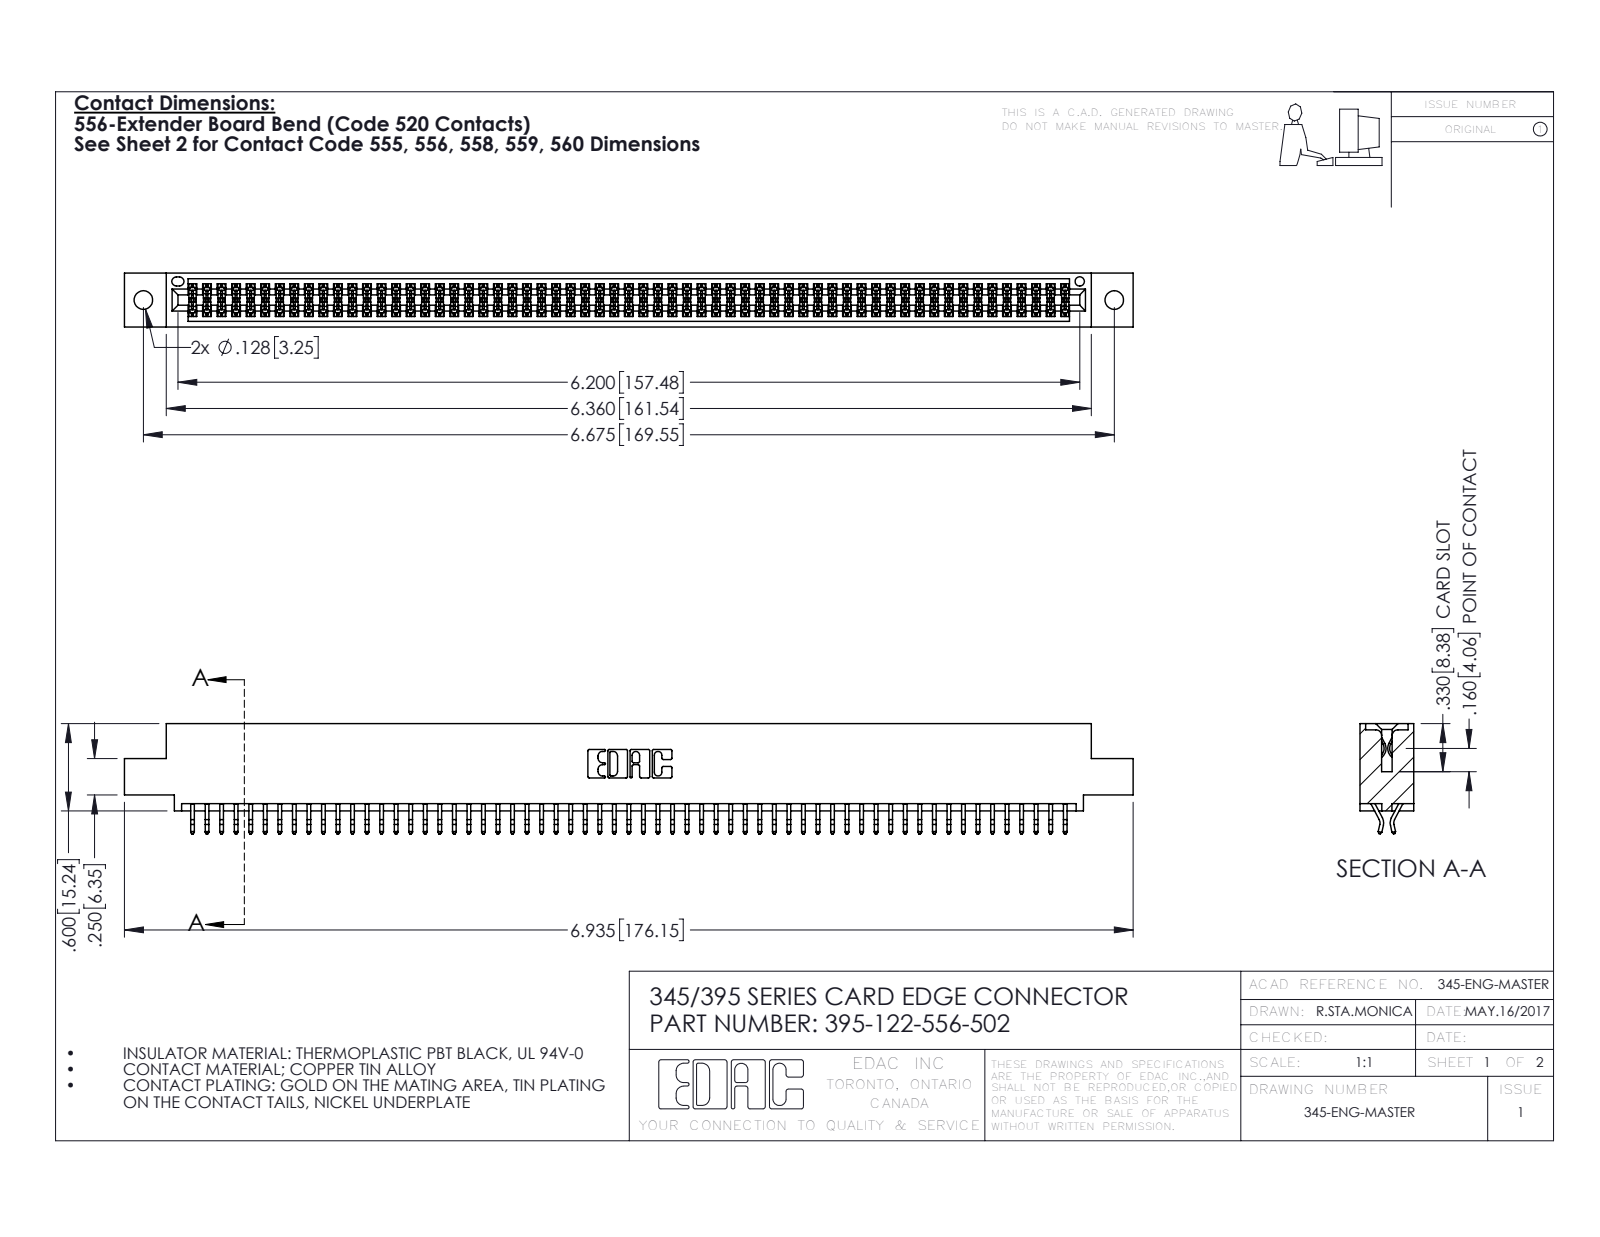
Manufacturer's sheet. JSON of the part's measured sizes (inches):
{"part_name": "395-122-556-502; 345 Part_0.110 Offset - 0.128 Dia; 345-292-001_556 Tail", "step_written_by": "SolidWorks 2016 (CONFIG_CONTROL_DESIGN)", "units": "inches", "bodies": {"solids": 123, "faces": 6962, "planar": 4598, "cylindrical": 2364, "other": 0}, "overall_size": [6.935, 0.757, 0.37], "volume_in3": 1.048, "surface_area_in2": 39.47, "round_holes": [[0.128, 2], [0.064, 1]], "partial_cylinders_radius": [[0.006, 183], [0.01, 22], [0.007, 6], [0.031, 6], [0.026, 3], [0.01, 2], [0.014, 2], [0.019, 2]], "face_to_face_distances": [0.298, 0.072, 0.37, 0.2, 0.025, 0.098, 0.272, 0.225, 0.175, 0.149], "hole_center_spacings": [0.27, 6.439, 6.675]}
